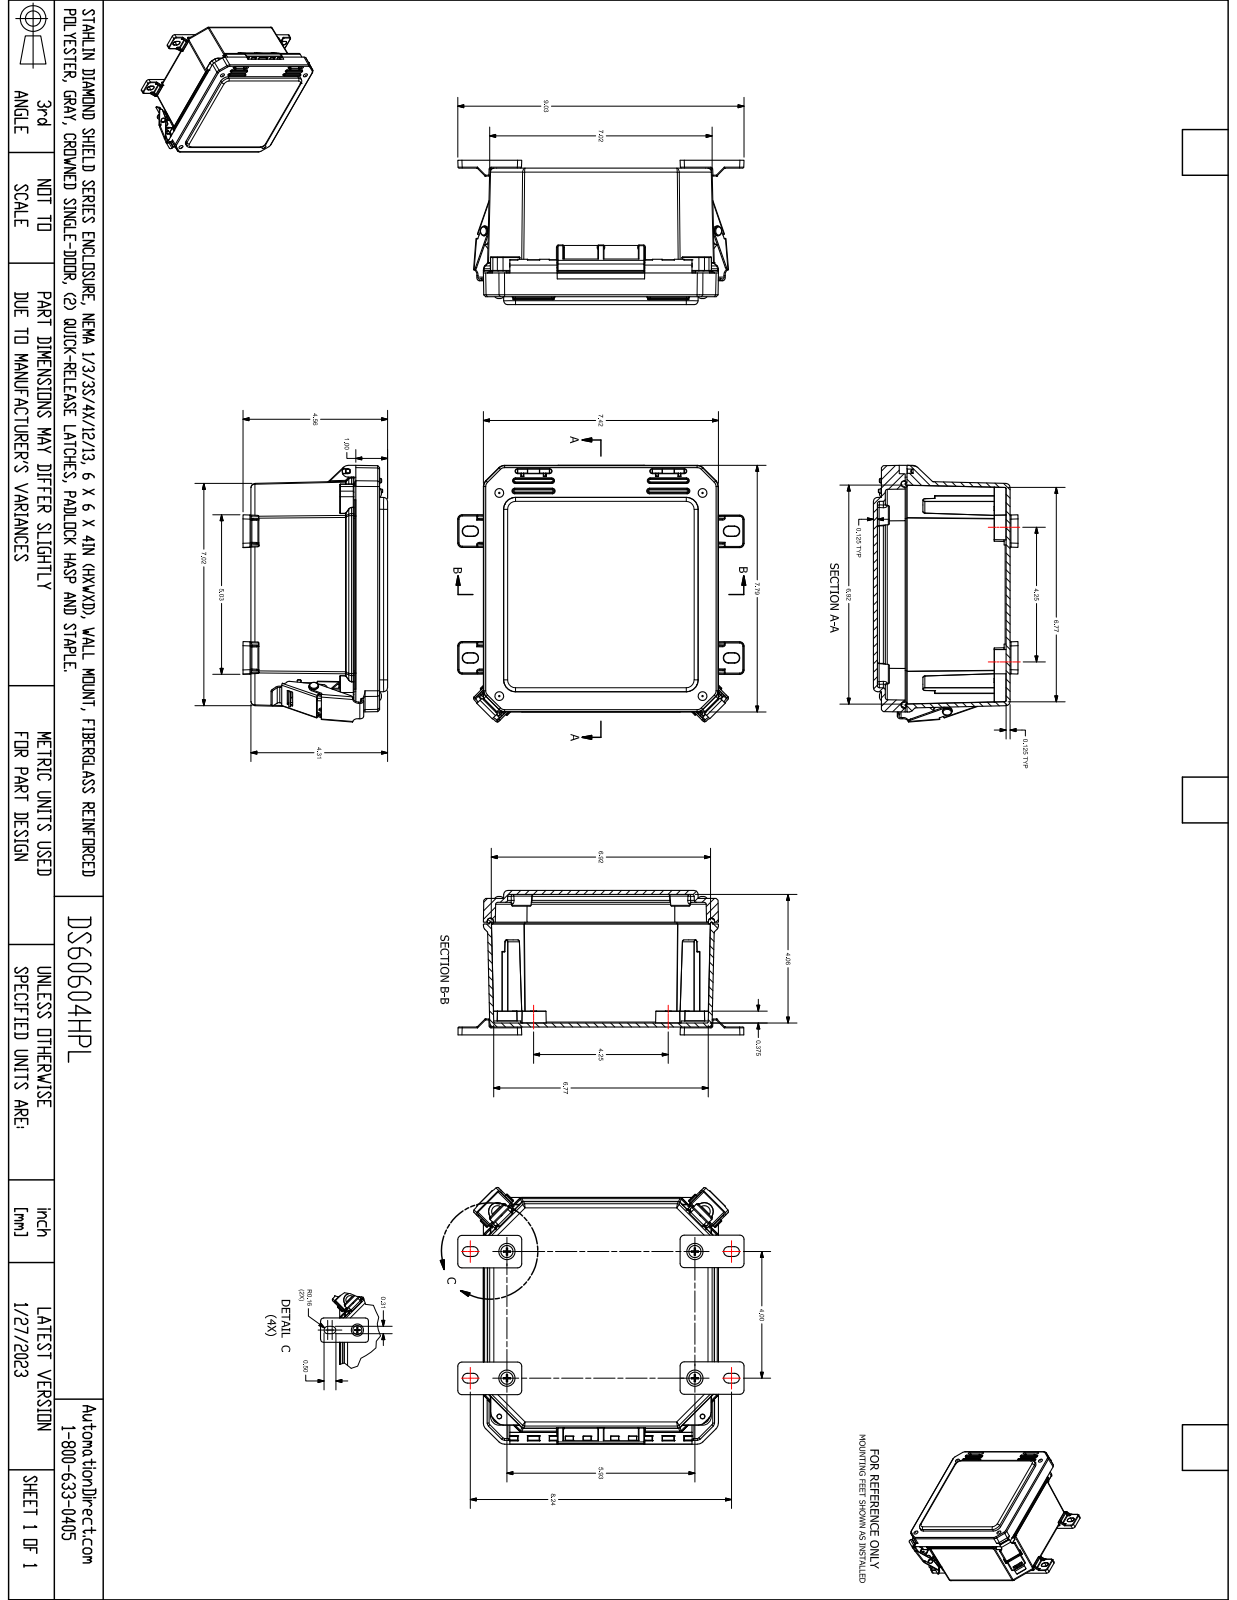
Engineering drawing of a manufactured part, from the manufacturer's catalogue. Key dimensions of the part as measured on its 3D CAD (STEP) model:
Part name (STEP PRODUCT): FR60604HPL
STEP written by: SolidWorks 2021 (AUTOMOTIVE_DESIGN)
Units: inches
Bodies: 29 solids, 2591 faces (730 planar, 1236 cylindrical, 625 other)
Overall size (bounding box): 8.106 × 8.042 × 4.51
Volume: 38.27 in³ · Surface area: 526.1 in²
Round holes (diameter × count): ⌀0.135 ×8, ⌀0.152 ×8, ⌀0.159 ×8, ⌀0.15 ×4, ⌀0.156 ×4, ⌀0.252 ×4, ⌀0.253 ×4, ⌀0.135 ×3, ⌀0.137 ×3, ⌀0.219 ×2, ⌀0.227 ×2, ⌀0.313 ×2
Round bosses / shafts (diameter × count): ⌀0.27 ×8, ⌀0.87 ×4, ⌀0.3 ×4, ⌀0.262 ×4, ⌀0.209 ×4, ⌀0.135 ×2, ⌀0.435 ×1, ⌀0.435 ×1
Partial cylindrical surfaces — rounded edges, fillets, slot ends (radius × count): R0.01 ×121, R0.005 ×94, R0.02 ×75, R0.03 ×71, R0.06 ×36, R0.09 ×26, R0.03 ×24, R0.096 ×24
Main face-to-face distances: 0.126, 0.125, 0.125, 4.185, 4.311, 4.06, 4.186, 0.25, 3.935, 4.061
Hole centre spacings: 6.414, 6.415, 6.415, 7.541, 0.25, 4.25, 5.44, 9.071
